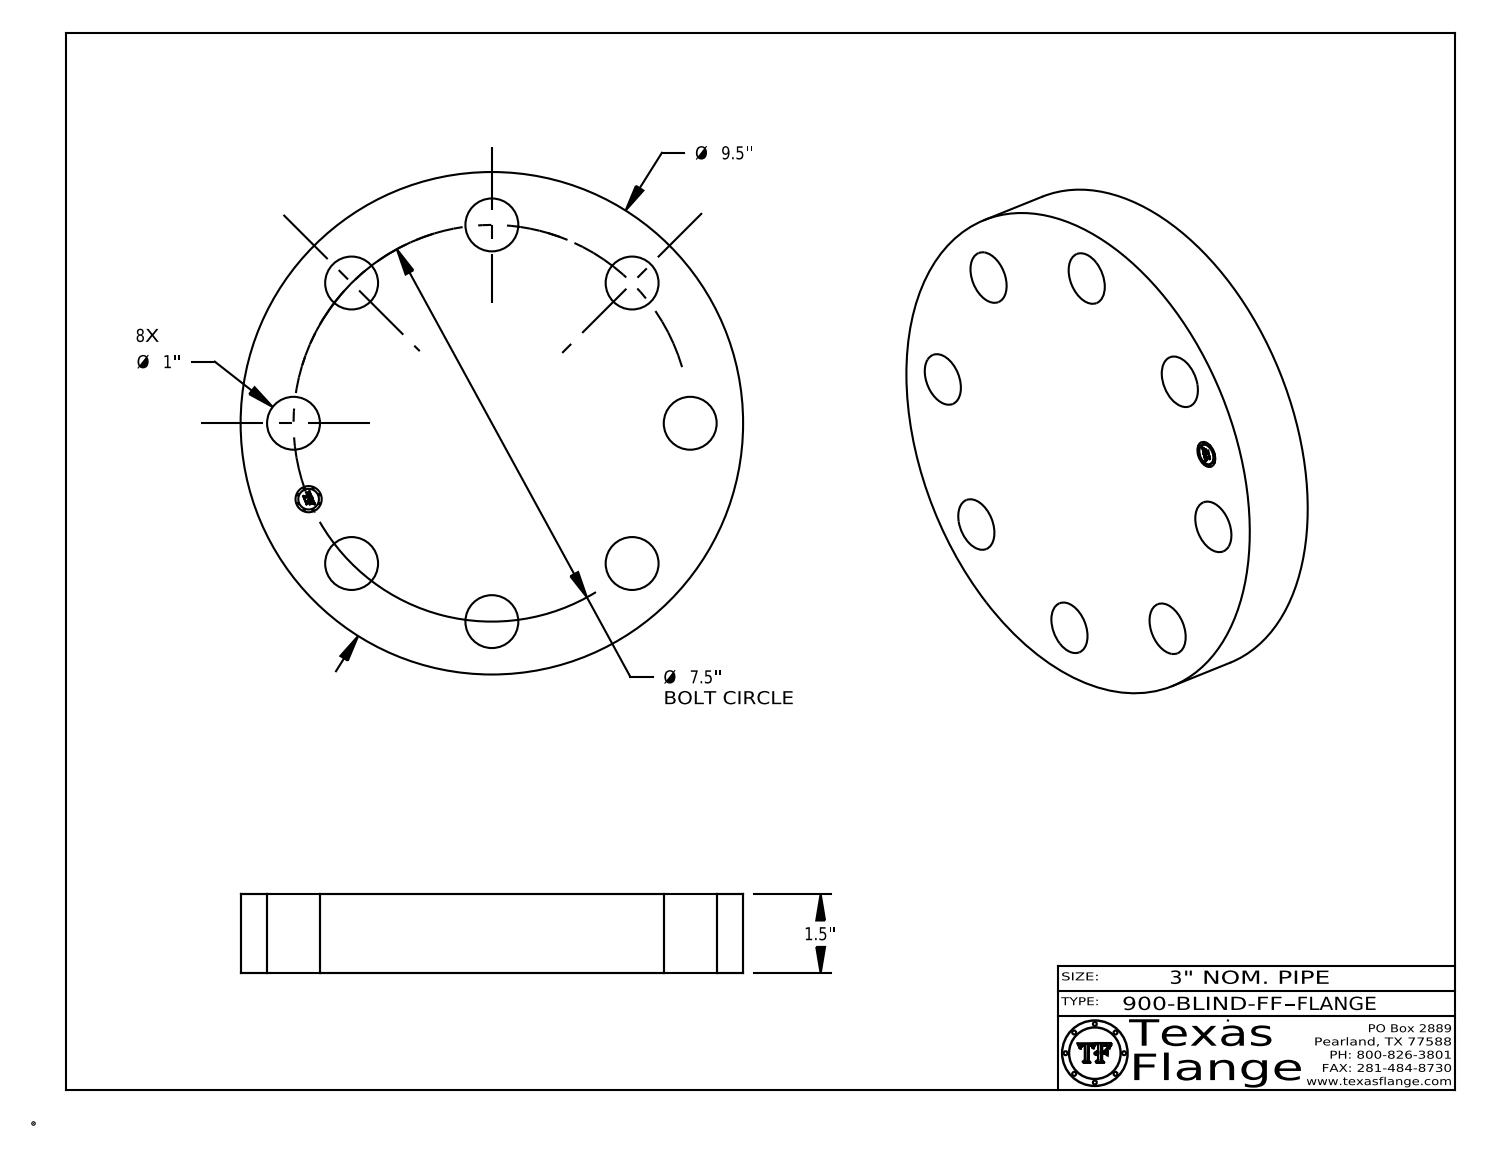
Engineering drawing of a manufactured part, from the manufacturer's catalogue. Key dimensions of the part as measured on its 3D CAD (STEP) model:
Part name (STEP PRODUCT): 900-BLIND-FF
STEP written by: CATIA V5 STEP AP214 (AUTOMOTIVE_DESIGN)
Units: inches
Bodies: 1 solid, 405 faces (367 planar, 38 cylindrical, 0 other)
Overall size (bounding box): 9.5 × 9.5 × 1.5
Volume: 96.9 in³ · Surface area: 211.8 in²
Round holes (diameter × count): ⌀1 ×8, ⌀0.495 ×1
Round bosses / shafts (diameter × count): ⌀0.03 ×8, ⌀9.5 ×1, ⌀0.39 ×1
Main face-to-face distances: 1.5, 0.015, 1.485, 0.148, 0.145, 0.027, 0.096, 0.122, 0.022, 0.101
Hole centre spacings: 2.87, 5.303, 6.929, 1.463, 6.236, 7.356, 7.5, 7.5
